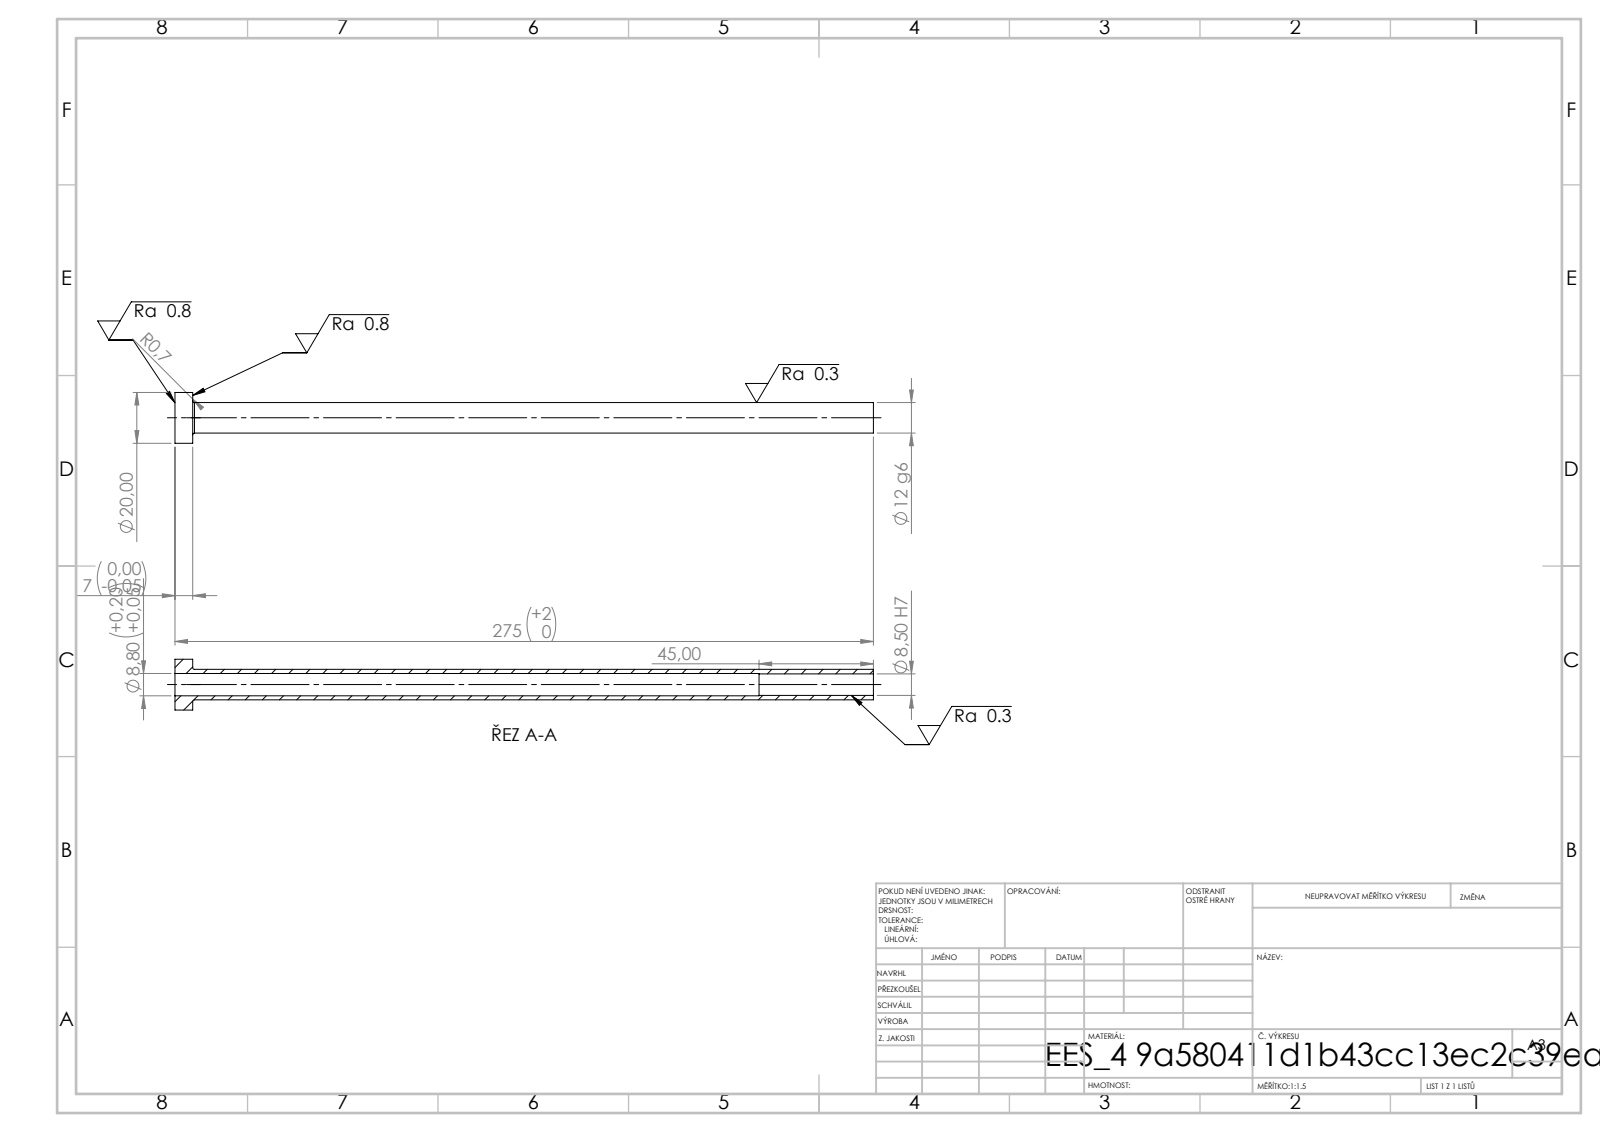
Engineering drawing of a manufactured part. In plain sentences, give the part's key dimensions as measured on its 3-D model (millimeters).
Its 3-D file was written by "SolidWorks 2019 (CONFIG_CONTROL_DESIGN)". It is 1 solid with 14 faces: 4 planar, 8 cylindrical and 2 other. Overall it measures 275 by 20 by 20 millimeters. Its volume is 15 971 cubic millimeters and its surface area 18 607 square millimeters. Round holes: 1 of diameter 8.5, 1 of diameter 8.8. Round bosses or shafts: 1 of diameter 20, 1 of diameter 12. The main face-to-face distances are 7, 275, 268, 230, 223, 45.
